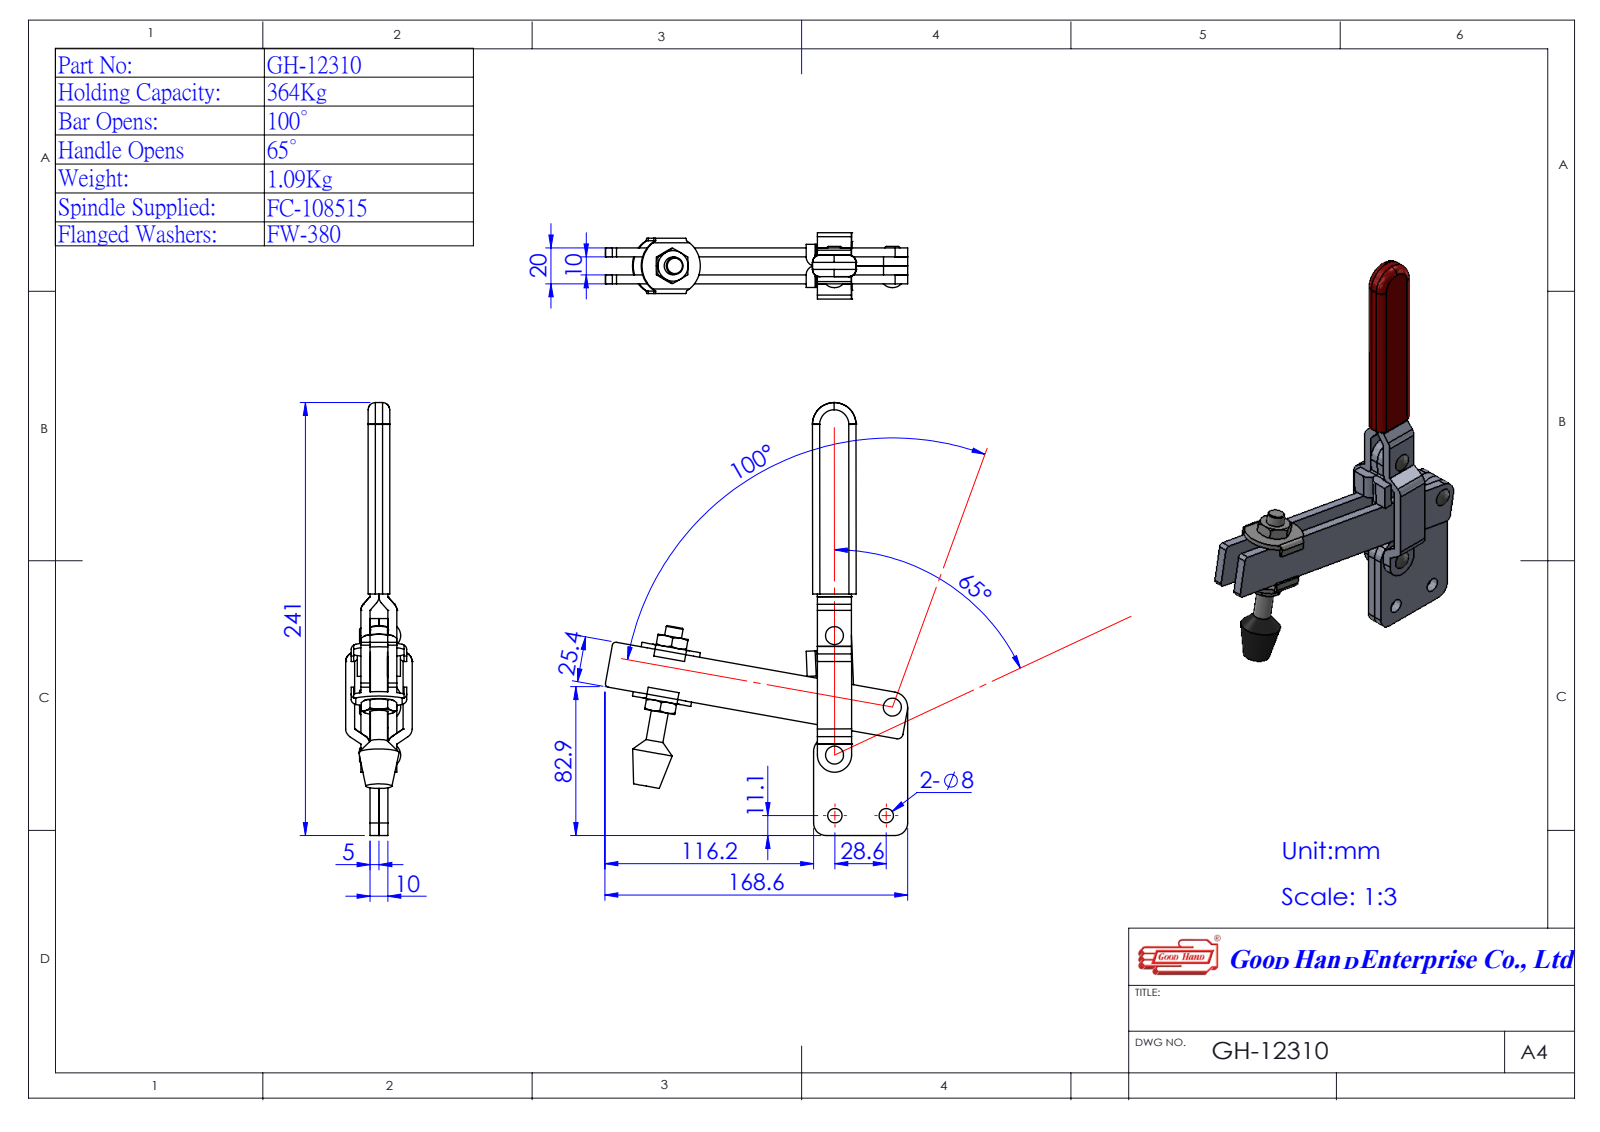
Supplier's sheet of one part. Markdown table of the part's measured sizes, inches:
| quantity | value |
| --- | --- |
| part name | Group4^GH-12310(簡化)-1; GH-12310(簡化)-1; Group3^GH-12310(簡化)-1; Group2^GH-12310(簡化)-1 (+2 more) |
| STEP written by | SolidWorks 2016 (AUTOMOTIVE_DESIGN) |
| units | inches |
| bodies | 5 solids, 298 faces (133 planar, 117 cylindrical, 48 other) |
| overall size | 9.464 × 6.666 × 1.457 |
| volume | 9.367 in³ |
| surface area | 94.4 in² |
| round holes (diameter × count) | 0.157 × 4, 0.315 × 2, 0.248 × 1 |
| round bosses / shafts (diameter × count) | 0.375 × 1, 0.248 × 1 |
| partial cylindrical surfaces (radius × count) | 0.004 × 10, 0.157 × 8, 0.039 × 4, 0.079 × 4, 0.1 × 4, 0.201 × 4, 0.201 × 4, 0.374 × 3 |
| main face-to-face distances | 0.197, 0.591, 0.394, 0.787, 0.335, 0.925, 0.157, 0.63, 0.039, 0.433 |
| hole center spacings | 1.126, 1.236, 1.27, 1.326, 1.351, 1.647, 1.745, 2.017 |
